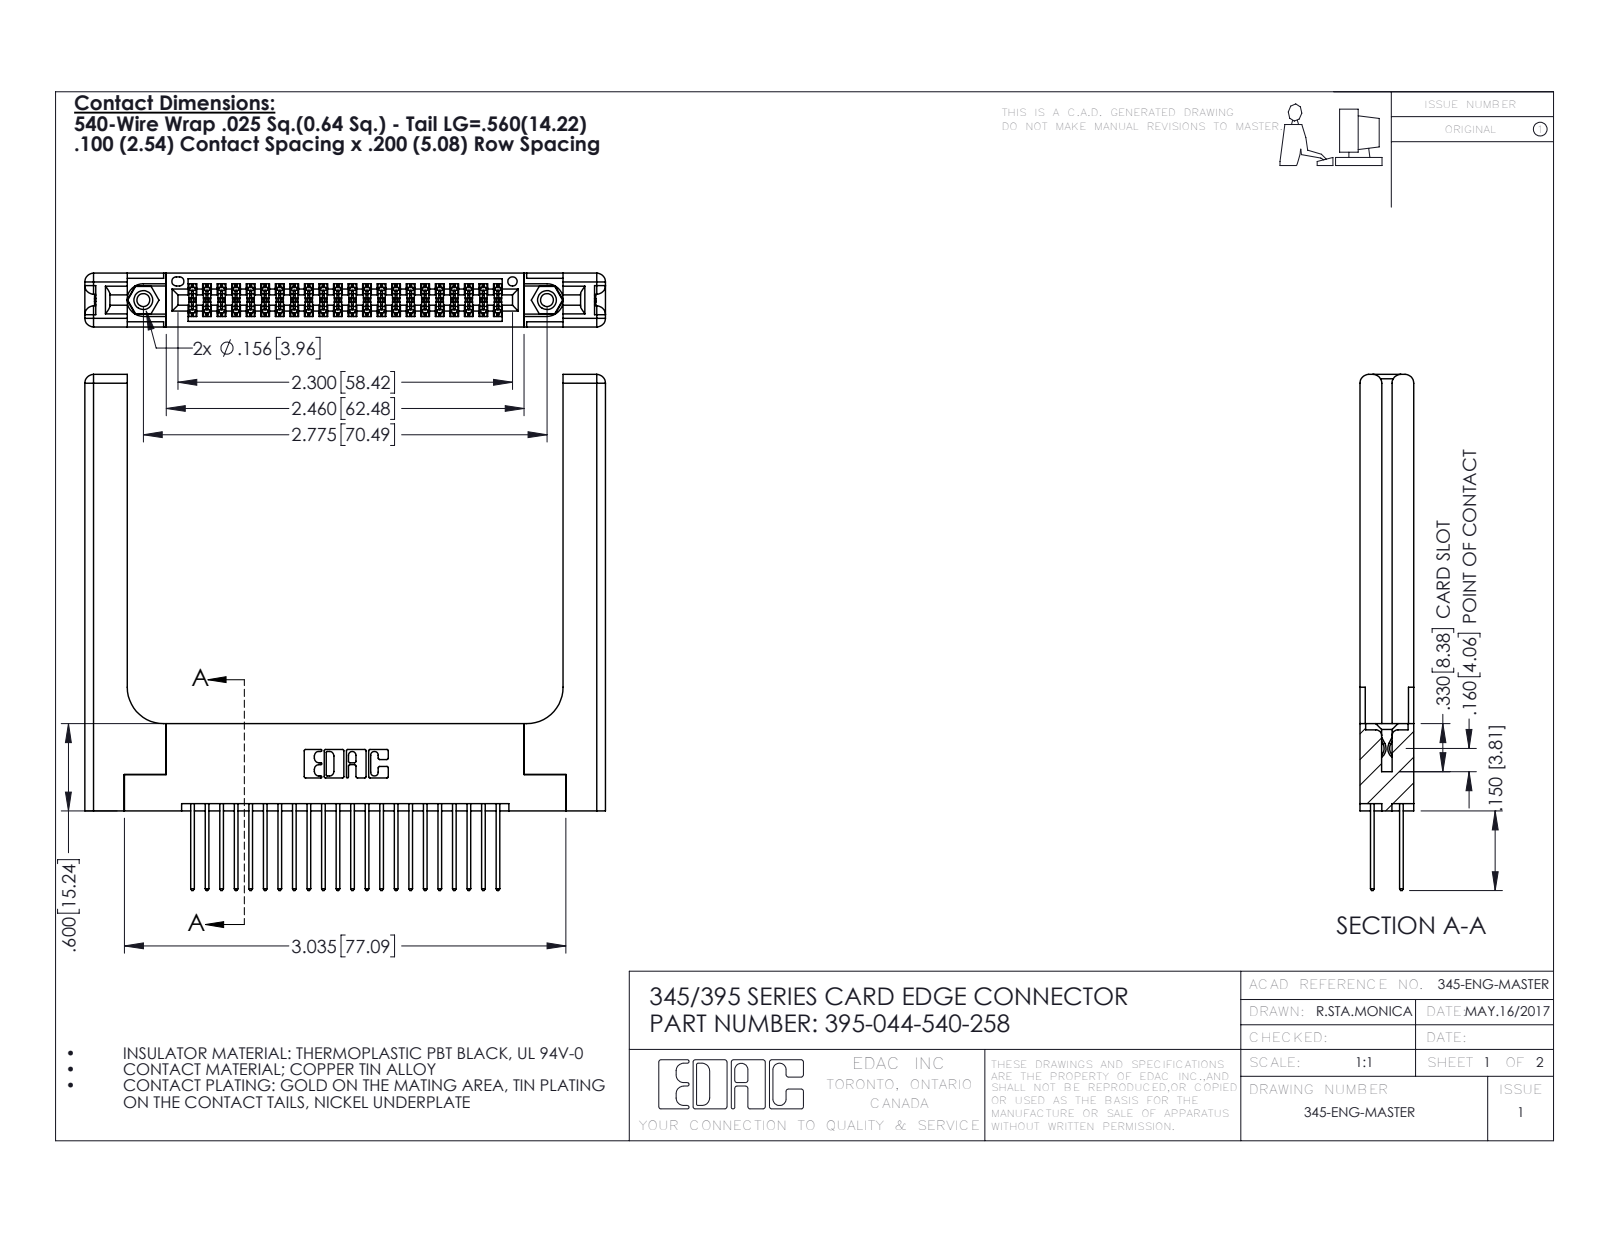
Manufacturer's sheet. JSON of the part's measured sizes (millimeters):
{"part_name": "345 Part_Flush Mounting Lugs - 0.156 Dia-TH; 345-220-058_345-220-058; 345-292-001_345-293-140; 395-044-540-258 (+1 more)", "step_written_by": "SolidWorks 2016 (CONFIG_CONTROL_DESIGN)", "units": "millimeters", "bodies": {"solids": 49, "faces": 2582, "planar": 1680, "cylindrical": 842, "other": 60}, "overall_size": [90.9, 90.1, 9.4], "volume_mm3": 17290, "surface_area_mm2": 18470, "round_holes": [[2.3, 2], [3.2, 2], [4, 2], [1.6, 1]], "round_bosses_or_shafts": [[3.9, 2]], "partial_cylinders_radius": [[0.2, 66], [0.3, 44], [0.3, 22], [1.5, 16], [0.2, 6], [0.8, 6], [0.7, 3], [0.4, 2]], "face_to_face_distances": [1.8, 9.4, 7.6, 5.1, 2.5, 6.9, 0.6, 5.7, 3.8, 3.8], "hole_center_spacings": [6.9, 64.5, 70.5]}
